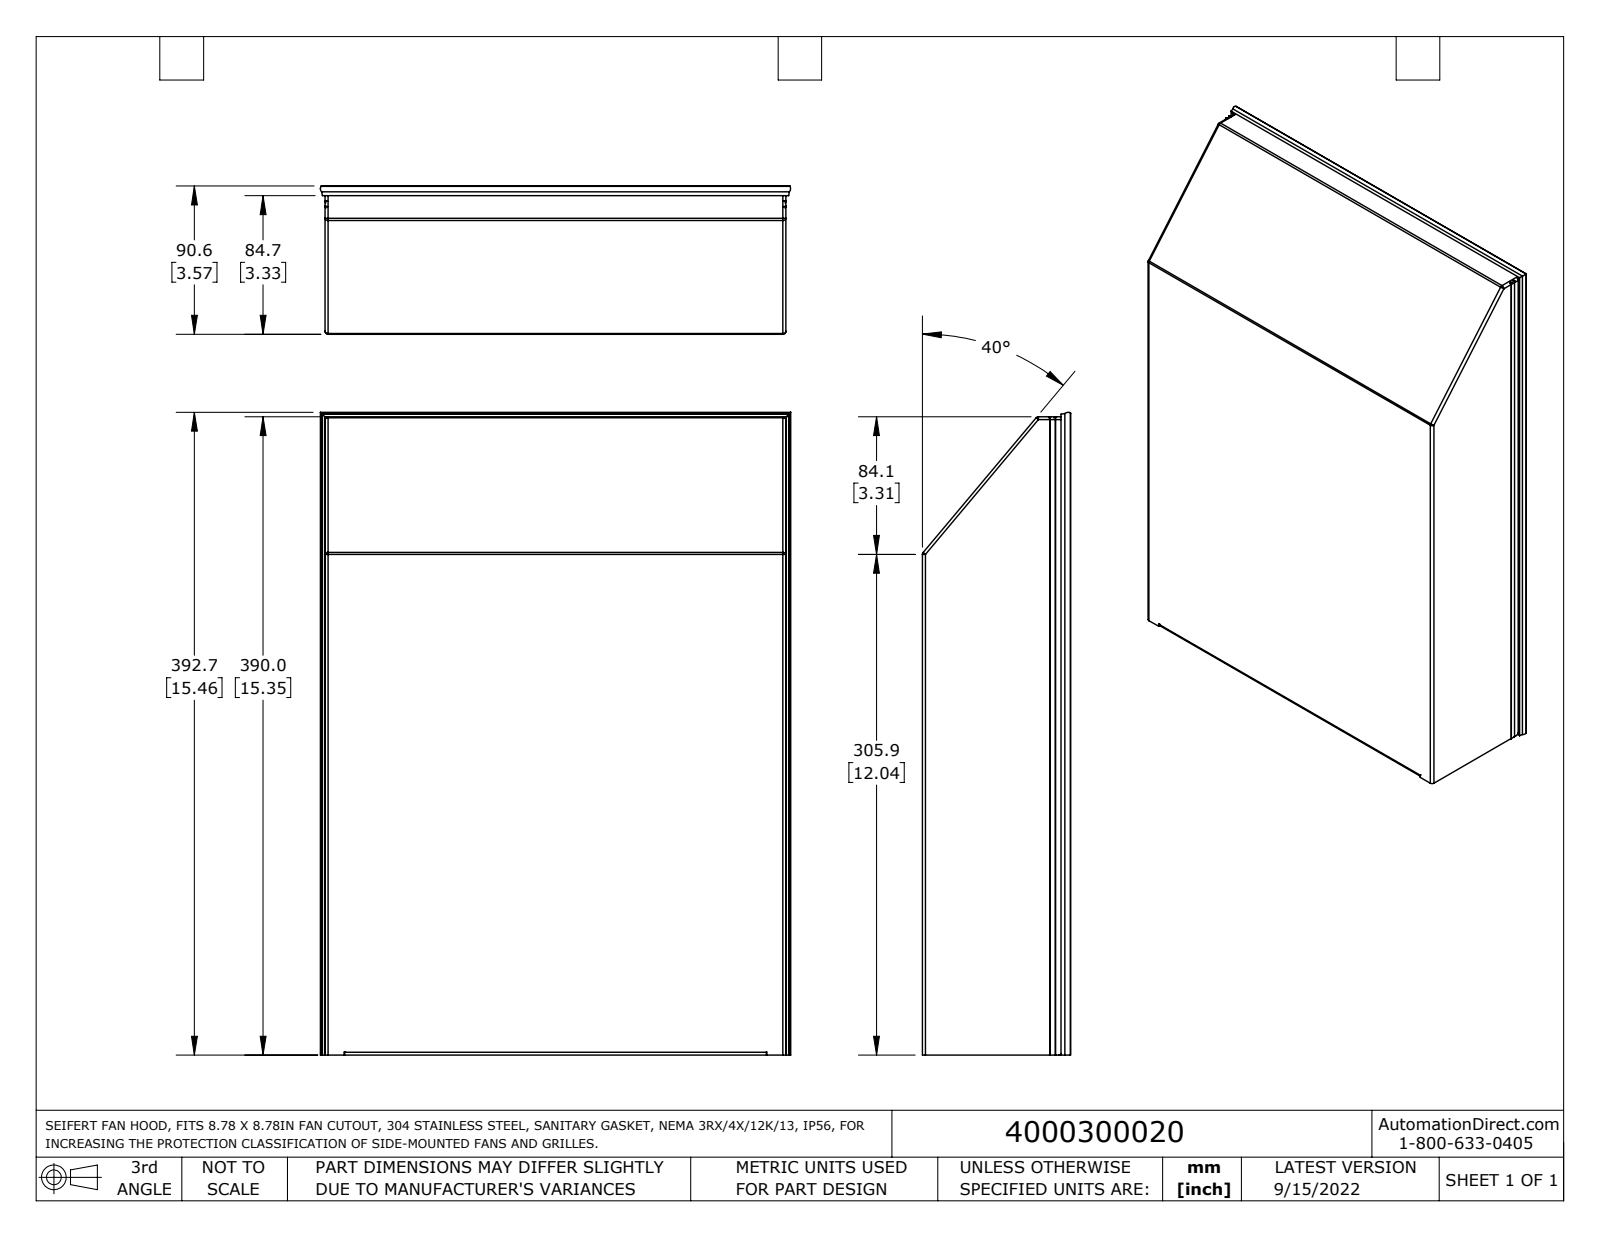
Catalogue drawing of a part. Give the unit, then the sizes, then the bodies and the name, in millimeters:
Units: millimetres
Overall size (bounding box): 392.7 × 287.4 × 90.6
Round holes (diameter × count): ⌀5.5 ×4
Partial cylindrical surfaces — rounded edges, fillets, slot ends (radius × count): R3 ×19, R0.1 ×12, R7.1 ×12, R30 ×12, R1.8 ×10, R0.2 ×9, R0.8 ×9, R1 ×6
Main face-to-face distances: 0.8, 280.8, 280, 281.6, 1.5, 8.6, 273, 7.8, 272.2, 10.1
Hole centre spacings: 218.5, 297, 368.7
Volume: 267 400 mm³ · Surface area: 498 600 mm²
Bodies: 4 solids, 309 faces (139 planar, 162 cylindrical, 8 other)
Part name (STEP PRODUCT): 45397
STEP written by: SolidWorks 2021 (CONFIG_CONTROL_DESIGN)
